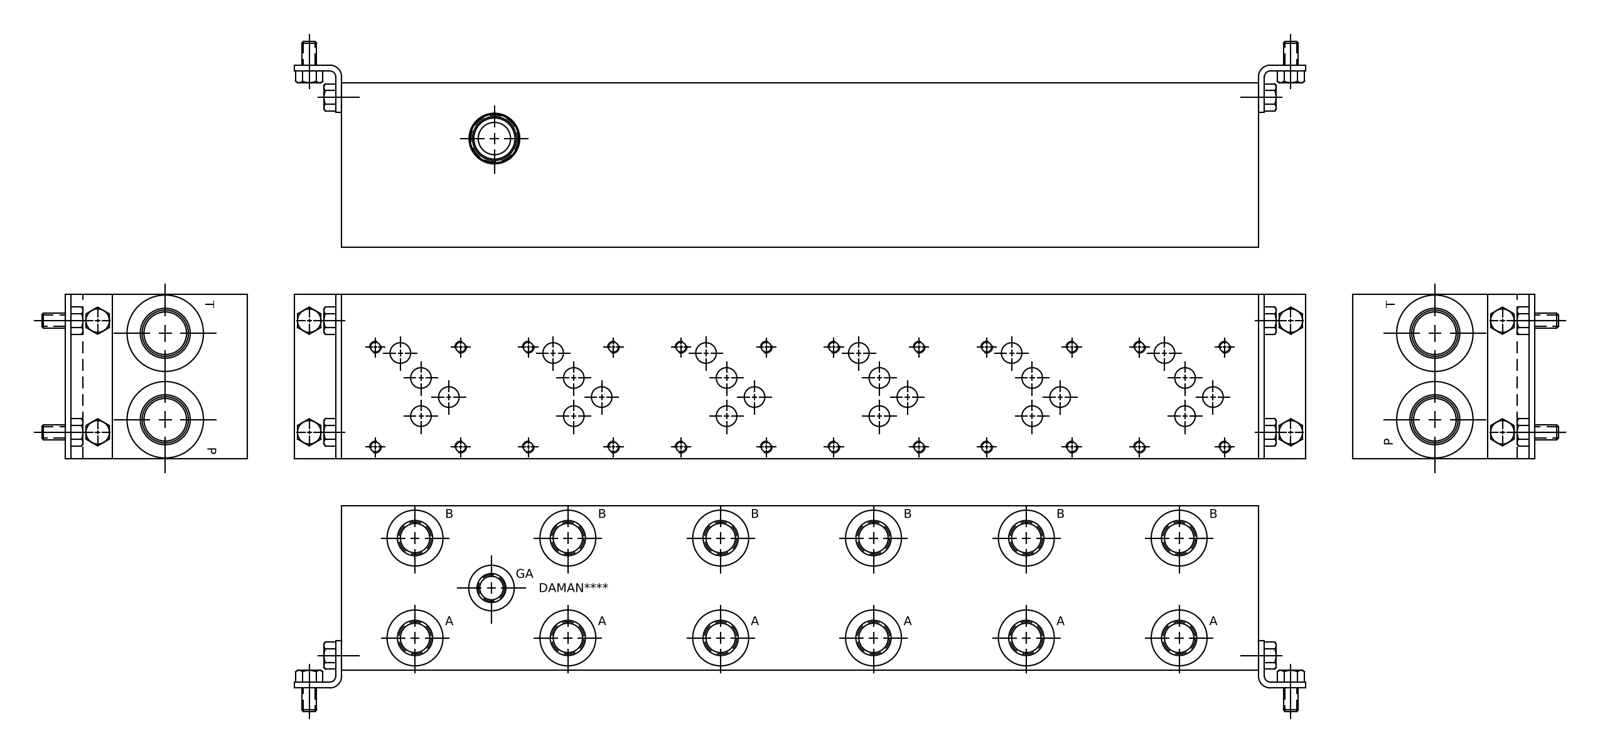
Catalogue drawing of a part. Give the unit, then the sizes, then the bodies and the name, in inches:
Units: inches
Overall size (bounding box): 19.5 × 3.5 × 3.5
Round holes (diameter × count): ⌀0.201 ×24, ⌀0.25 ×24, ⌀0.438 ×24, ⌀0.625 ×12, ⌀0.689 ×12, ⌀0.75 ×12, ⌀0.758 ×12, ⌀1.206 ×12, ⌀0.257 ×2, ⌀0.312 ×2, ⌀0.906 ×2, ⌀0.981 ×2
Main face-to-face distances: 3.5, 0.031, 3.469, 19.5, 19.469, 19.438, 0.75, 0.562, 0.593, 2.907
Hole centre spacings: 3.25, 6.5, 9.75, 3.883, 9.979, 6.839, 1.813, 2.125
Volume: 226 in³ · Surface area: 369.6 in²
Bodies: 1 solid, 1037 faces (498 planar, 171 cylindrical, 368 other)
Part name (STEP PRODUCT): Part_AD05P063S_S_3D
STEP written by: Autodesk Inventor 2020 (CONFIG_CONTROL_DESIGN)
